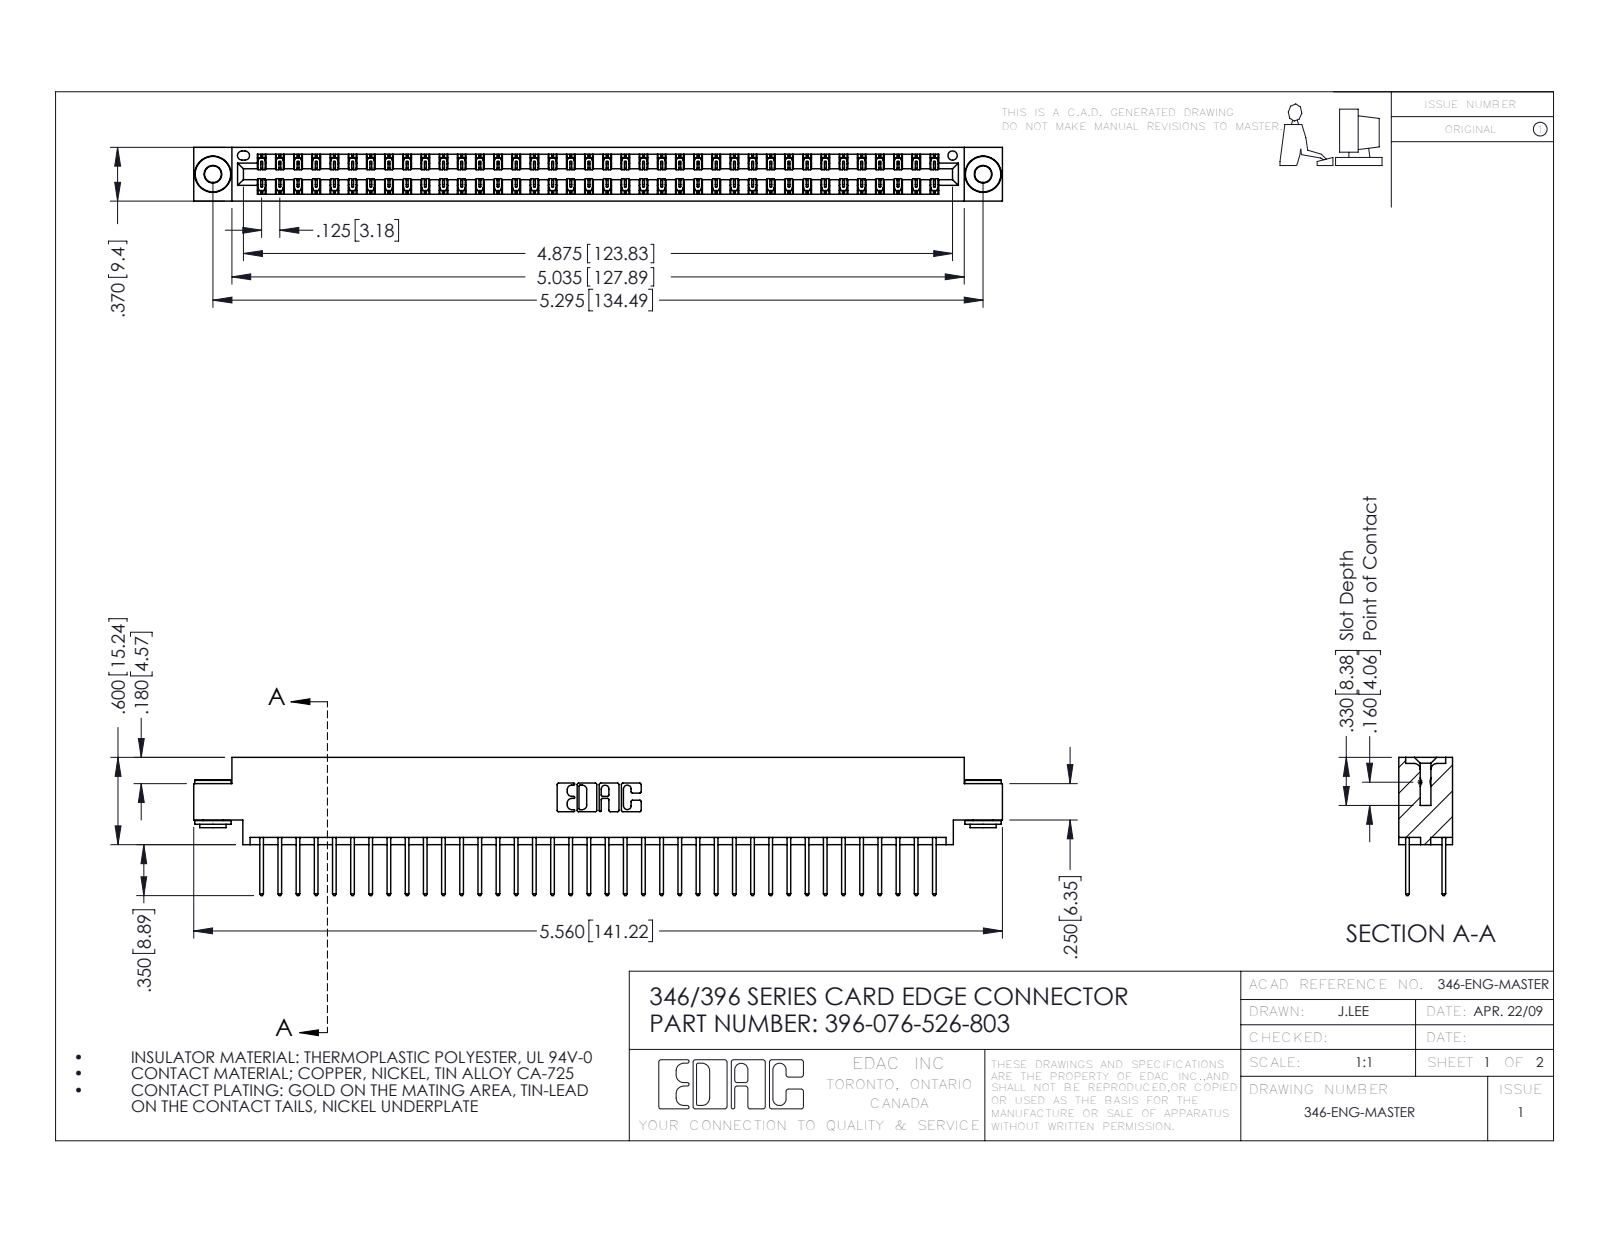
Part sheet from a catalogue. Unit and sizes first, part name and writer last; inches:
Units: inches
Overall size (bounding box): 5.56 × 0.95 × 0.37
Round holes (diameter × count): ⌀0.116 ×2, ⌀0.156 ×2, ⌀0.064 ×1
Round bosses / shafts (diameter × count): ⌀0.25 ×2, ⌀0.18 ×2, ⌀0.136 ×2
Partial cylindrical surfaces — rounded edges, fillets, slot ends (radius × count): R0.006 ×114, R0.01 ×76, R0.01 ×22, R0.007 ×6, R0.031 ×6, R0.026 ×3, R0.014 ×2, R0.022 ×2
Main face-to-face distances: 0.048, 0.322, 0.25, 0.37, 0.025, 0.072, 0.298, 0.275, 0.148, 0.222
Hole centre spacings: 0.246, 5.086, 5.295
Volume: 0.838 in³ · Surface area: 30.63 in²
Bodies: 79 solids, 4116 faces (2750 planar, 1358 cylindrical, 8 other)
Part name (STEP PRODUCT): 345-250-002_345-250-002-102; 346 Part_0.170 Offset - 0.156 Dia-TH; 396-076-526-803; 345-292-001_345-293-126
STEP written by: SolidWorks 2016 (CONFIG_CONTROL_DESIGN)
